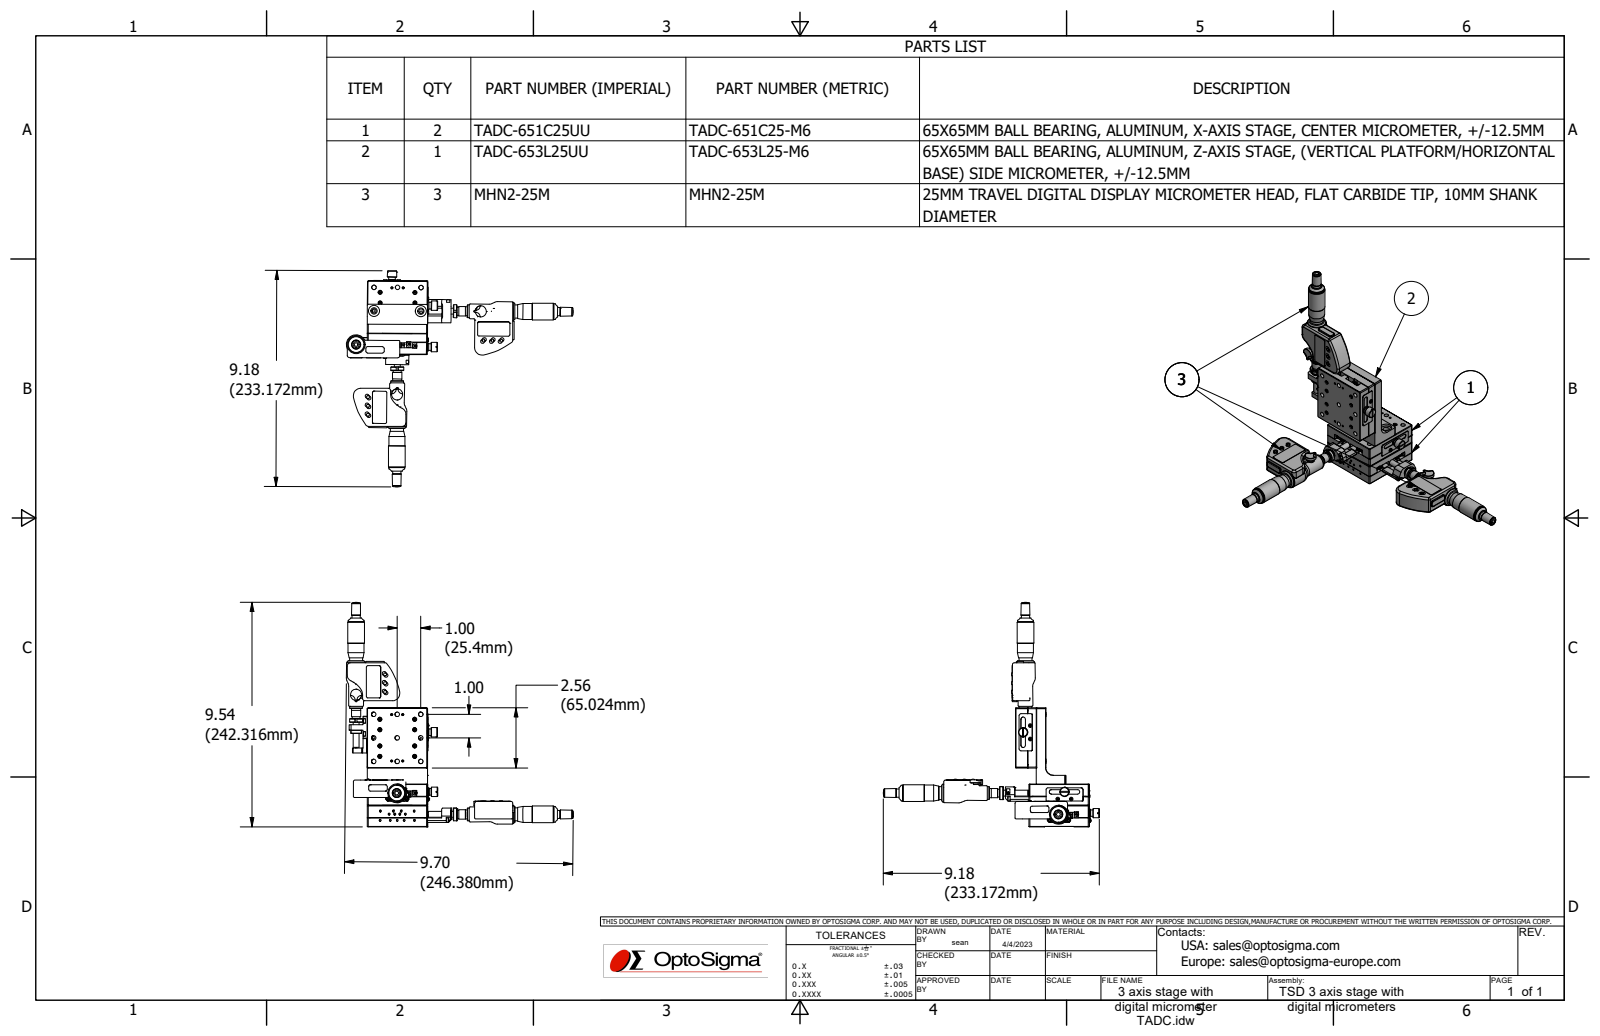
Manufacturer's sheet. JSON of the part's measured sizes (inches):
{"part_name": "3 axis stage with digital micrometer TADC; TADC-652WC25UU; TADC651C25UU-M02-13001-S04; TADC652WC25UU-M02-13001-S01 (+5 more)", "step_written_by": "Autodesk Inventor 2022 (AUTOMOTIVE_DESIGN)", "units": "inches", "bodies": {"solids": 14, "faces": 3752, "planar": 2100, "cylindrical": 954, "other": 698}, "overall_size": [9.644, 9.537, 9.183], "volume_in3": 30.06, "surface_area_in2": 284.7, "round_holes": [[0.118, 62], [0.11, 54], [0.079, 51], [0.094, 48], [0.165, 24], [0.169, 24], [0.196, 18], [0.083, 16], [0.062, 14], [0.062, 12], [0.276, 10], [0.472, 10]], "round_bosses_or_shafts": [[0.079, 60], [0.15, 48], [0.177, 28], [0.059, 20], [0.098, 14], [0.118, 12], [0.102, 12], [0.394, 11]], "partial_cylinders_radius": [[0.079, 39], [0.039, 24], [0.098, 20], [0.02, 15], [0.059, 12], [0.197, 11], [0.008, 6], [0.094, 6]], "face_to_face_distances": [0.906, 0.394, 0.374, 0.894, 1.28, 0.512, 0.531, 0.606, 0.287, 0.618], "hole_center_spacings": [0.961, 0.551, 0.428, 0.463, 0.194, 0.272, 1.223, 1.487]}
